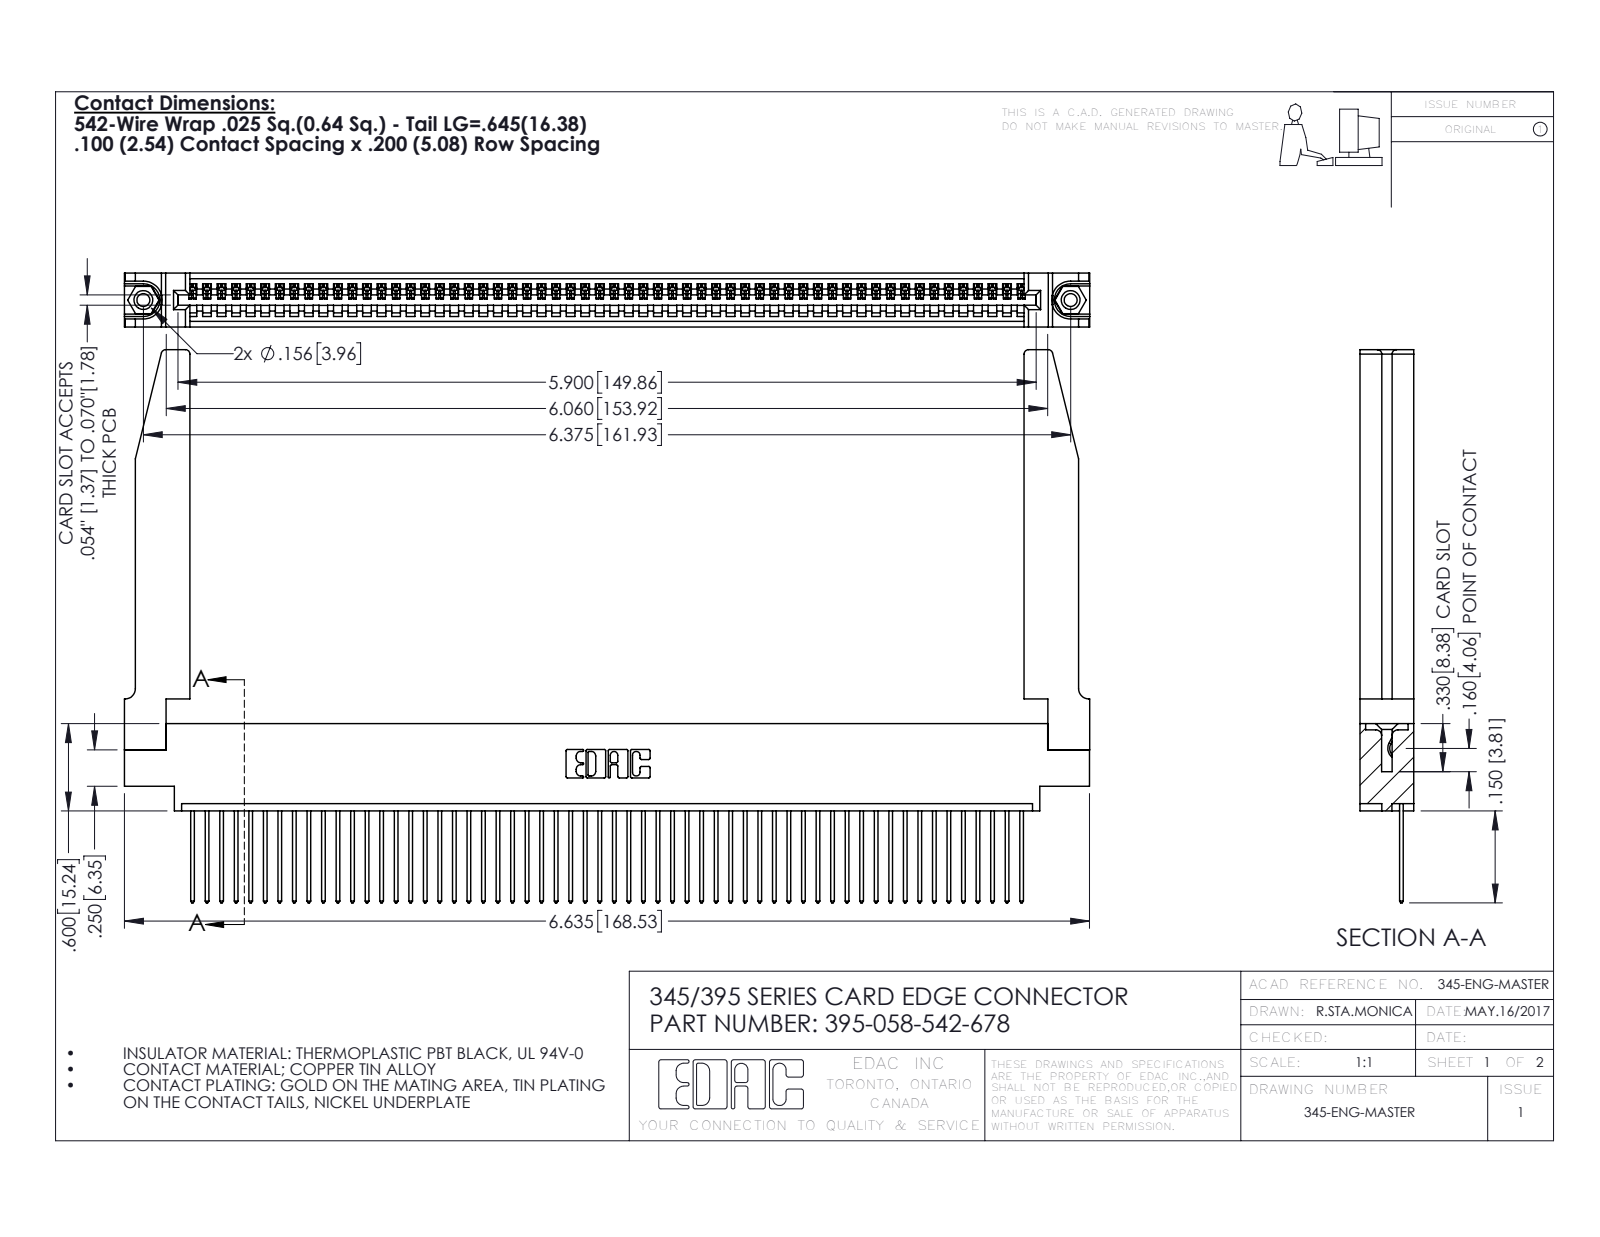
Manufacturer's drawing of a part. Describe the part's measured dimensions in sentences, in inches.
The part is named "345 Part_0.170 Offset - 0.156 Dia-TH; 395-058-542-678; 345-292-001_345-293-142; 345-220-078_345-220-078 (+1 more)". Its 3-D file was written by "SolidWorks 2016 (CONFIG_CONTROL_DESIGN)". It is 63 solids with 3728 faces: 2546 planar, 1130 cylindrical and 52 other. Overall it measures 6.636 by 3.802 by 0.37 inches. Its volume is 1.46 cubic inches and its surface area 45.69 square inches. Round holes: 2 of diameter 0.089, 2 of diameter 0.125, 2 of diameter 0.156, 1 of diameter 0.064. Round bosses or shafts: 2 of diameter 0.155. Partial cylindrical surfaces (rounded edges, fillets, slot ends): 116 of radius 0.006, 116 of radius 0.01, 22 of radius 0.01, 8 of radius 0.03, 6 of radius 0.007, 6 of radius 0.031, 3 of radius 0.026, 2 of radius 0.031. The main face-to-face distances are 0.072, 0.37, 0.298, 0.098, 0.272, 0.025, 0.2, 0.225, 0.15, 0.148. The hole center spacings are 0.27, 6.139, 6.375.
